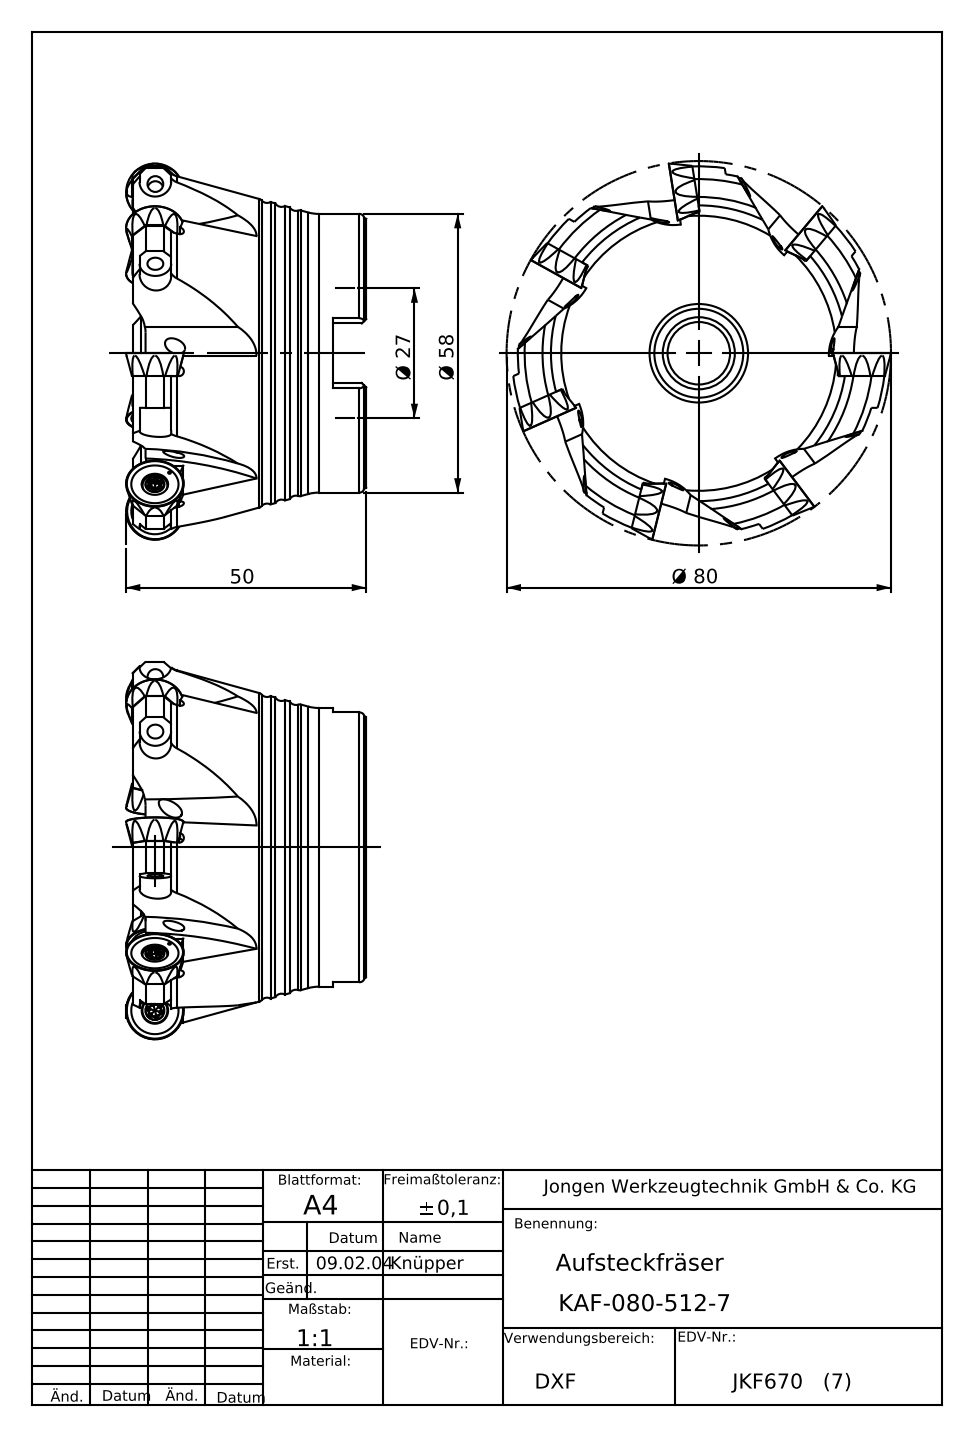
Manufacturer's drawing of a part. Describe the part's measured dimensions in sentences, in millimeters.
The part is named "KAF-080-512-7". Its 3-D file was written by "SolidWorks 2013 (AUTOMOTIVE_DESIGN)". It is 1 solid with 145 faces: 80 planar, 20 cylindrical and 45 other. Overall it measures 79.92 by 79.92 by 50.01 millimeters. Its volume is 138 069 cubic millimeters and its surface area 24 571 square millimeters. Round holes: 7 of diameter 3, 1 of diameter 13, 1 of diameter 18.5, 1 of diameter 27, 1 of diameter 27.15, 1 of diameter 27.3. Round bosses or shafts: 1 of diameter 58. Partial cylindrical surfaces (rounded edges, fillets, slot ends): 7 of radius 1. The main face-to-face distances are 45.96, 25, 20.96, 7, 18, 38.96, 12.4, 31.96, 24.96, 6.96.
